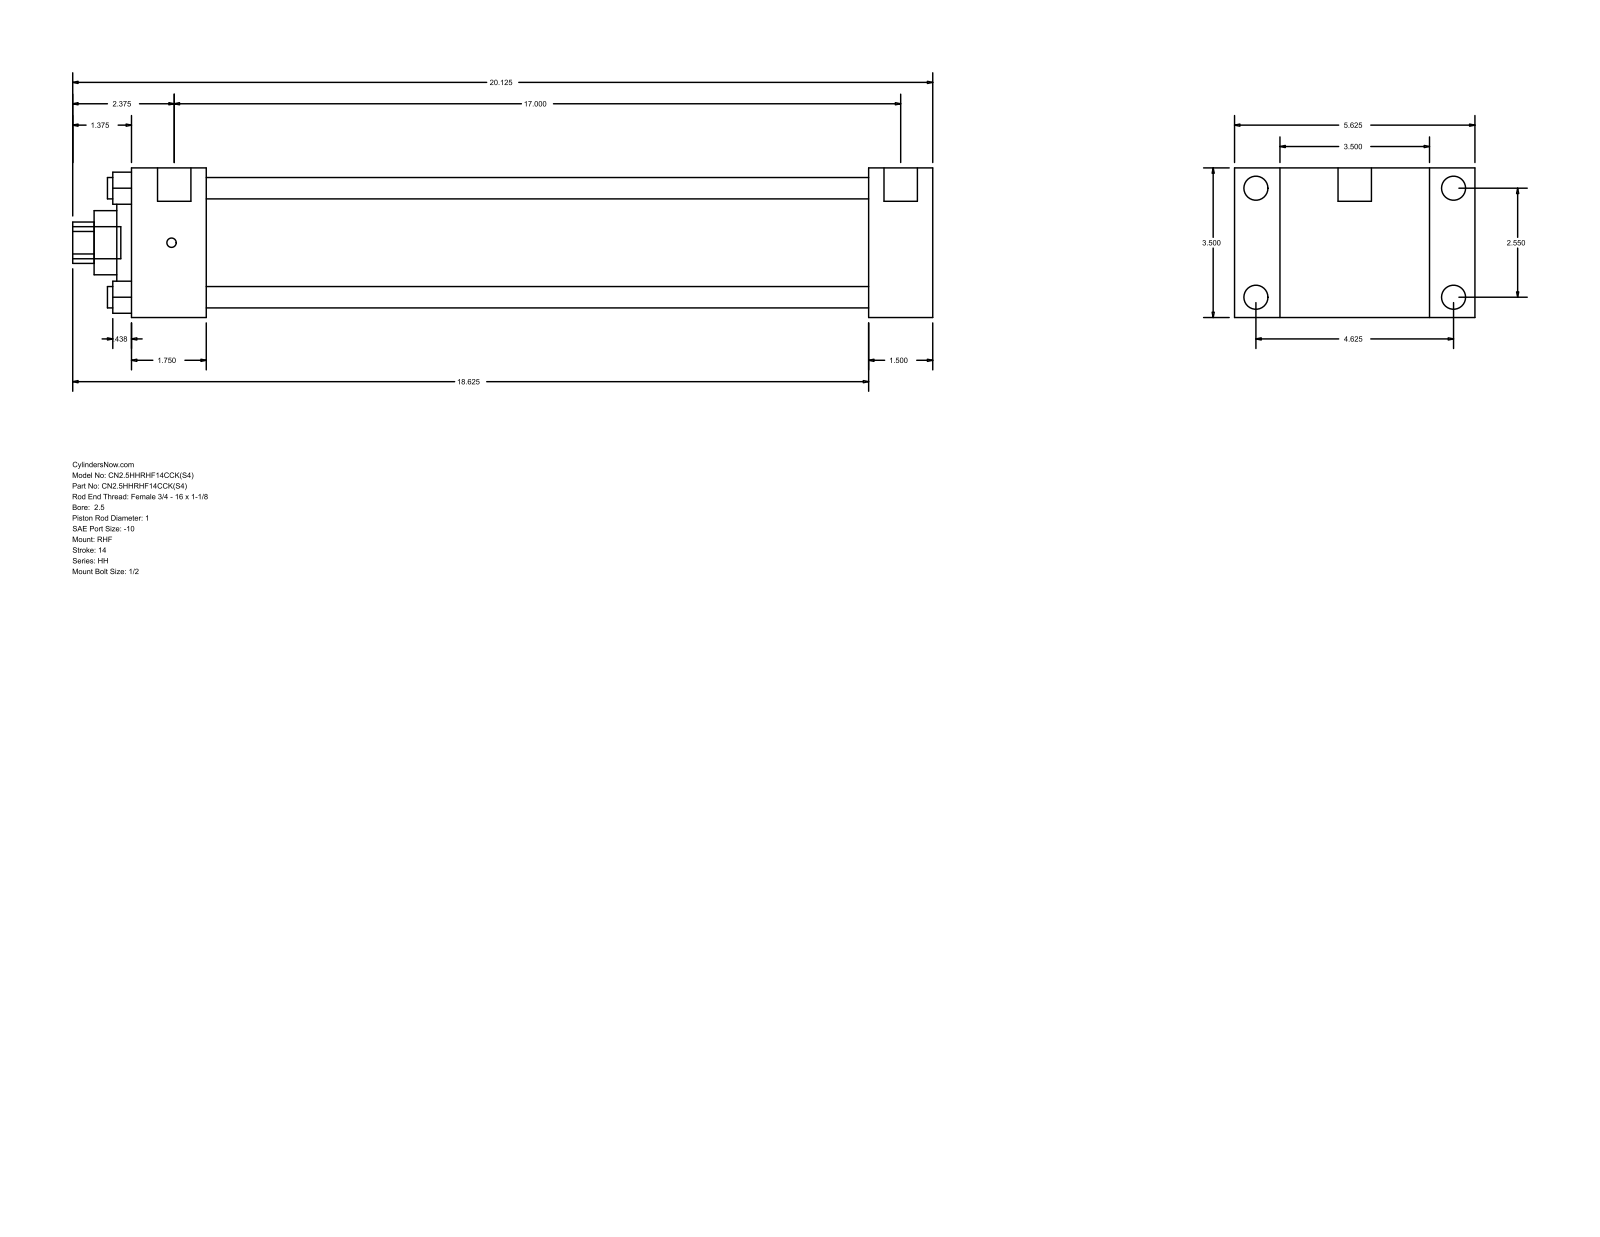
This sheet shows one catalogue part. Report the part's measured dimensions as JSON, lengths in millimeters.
{"part_name": "HH_RHF__0250_1", "step_written_by": "GSSL Pune (CONFIG_CONTROL_DESIGN)", "units": "millimeters", "bodies": {"solids": 0, "faces": 90, "planar": 61, "cylindrical": 29, "other": 0}, "overall_size": [511.18, 142.88, 88.9], "round_holes": [[12.7, 4], [25.4, 1], [38.1, 1], [60.33, 1], [73.03, 1]], "round_bosses_or_shafts": [[14.3, 4], [5.56, 4], [19.84, 2], [19.05, 1]], "partial_cylinders_radius": [[12.29, 1]], "face_to_face_distances": [88.9, 38.11, 26.99, 115.89, 438.15, 476.26, 142.88, 44.46, 393.69, 431.8], "hole_center_spacings": [45.79, 64.76, 91.58]}
